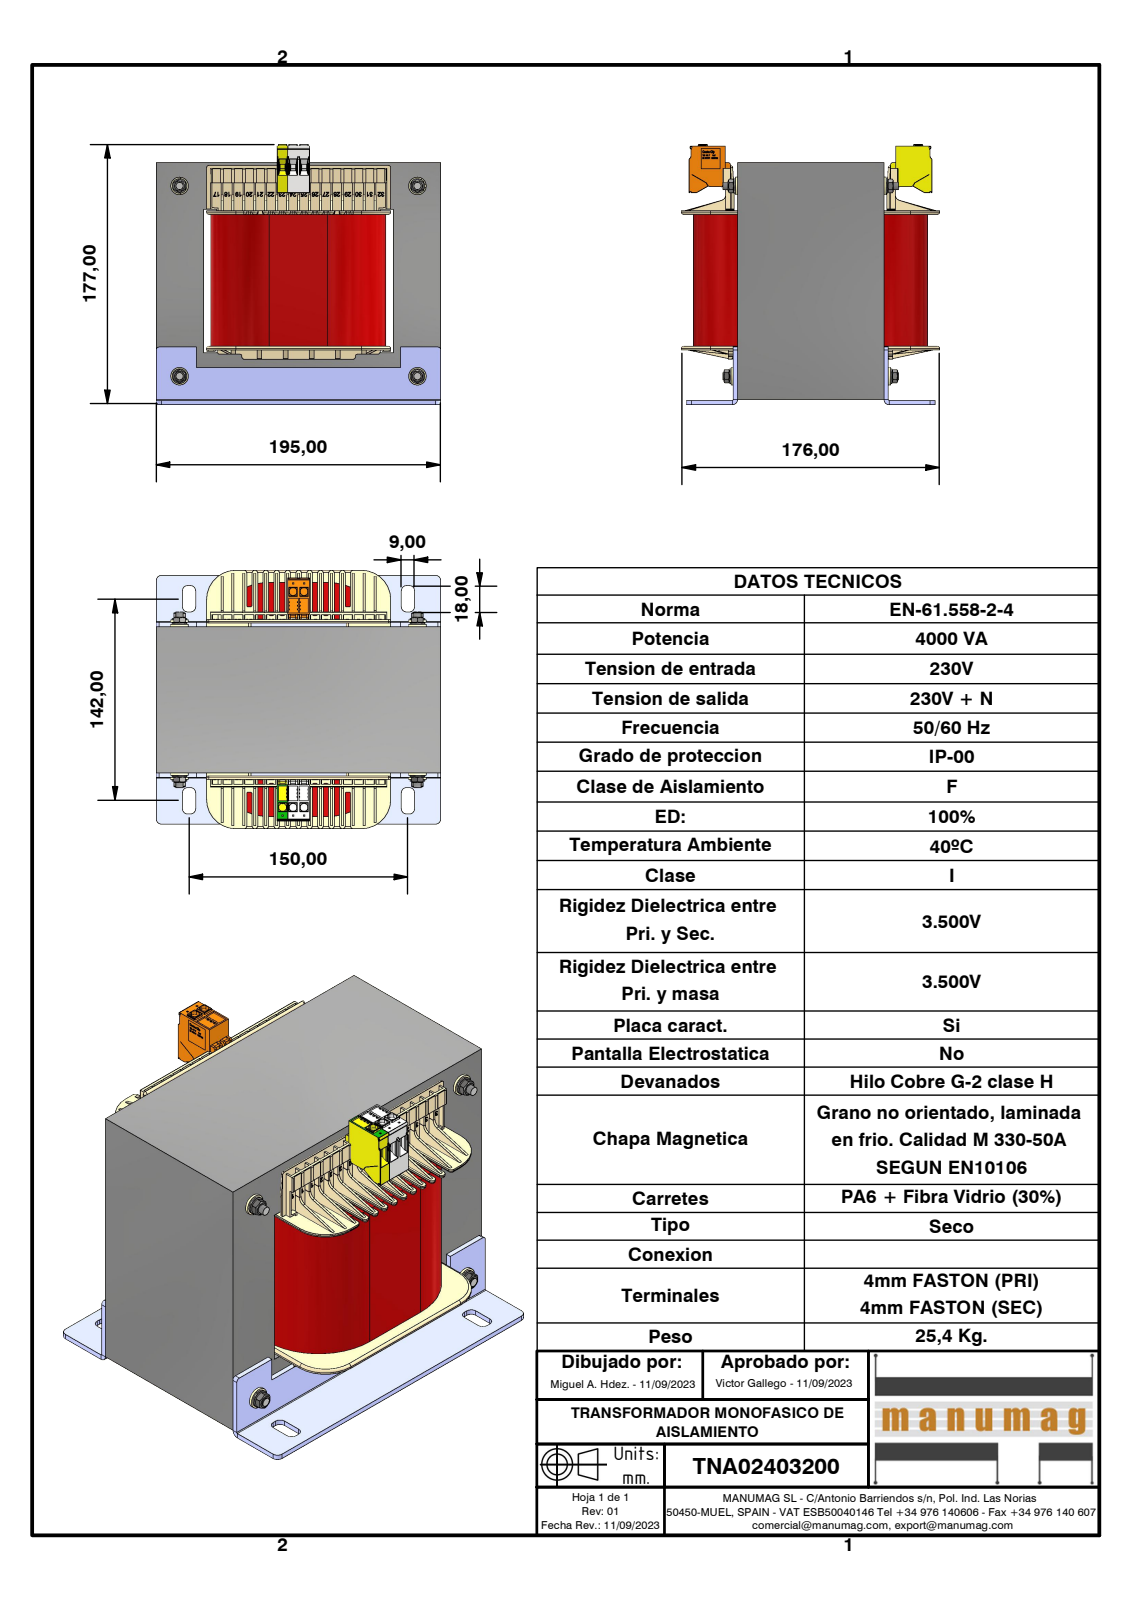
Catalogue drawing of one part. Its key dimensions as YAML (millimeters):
part_name: "TNA02403200; EI195 x 162 - 100 (Rc65); EI192_104_AK_25373_2_Wz837 BOBINADO; EI192_104_AK_25373_2_Wz837 (+8 more)"
step_written_by: "Autodesk Inventor 2023 (AUTOMOTIVE_DESIGN)"
units: millimeters
bodies: {solids: 36, faces: 7337, planar: 5195, cylindrical: 820, other: 1322}
overall_size: [195, 178, 176.6]
volume: 3681000
surface_area: 524400
round_holes:
  - {diameter: 4.1, count: 4}
  - {diameter: 5, count: 4}
  - {diameter: 5.3, count: 4}
  - {diameter: 11, count: 4}
  - {diameter: 9.9, count: 2}
round_bosses_or_shafts:
  - {diameter: 12, count: 4}
  - {diameter: 10, count: 4}
  - {diameter: 5.9, count: 4}
partial_cylinders:
  - {radius: 0.2, count: 188}
  - {radius: 0.2, count: 74}
  - {radius: 1, count: 52}
  - {radius: 1.5, count: 44}
  - {radius: 0.5, count: 30}
  - {radius: 2, count: 22}
  - {radius: 3.5, count: 22}
  - {radius: 0.3, count: 12}
face_to_face_distances: [32.5, 130, 3, 162.5, 2.4, 100, 65, 92.6, 2, 97.5]
hole_center_spacings: [130, 163, 208.5]
